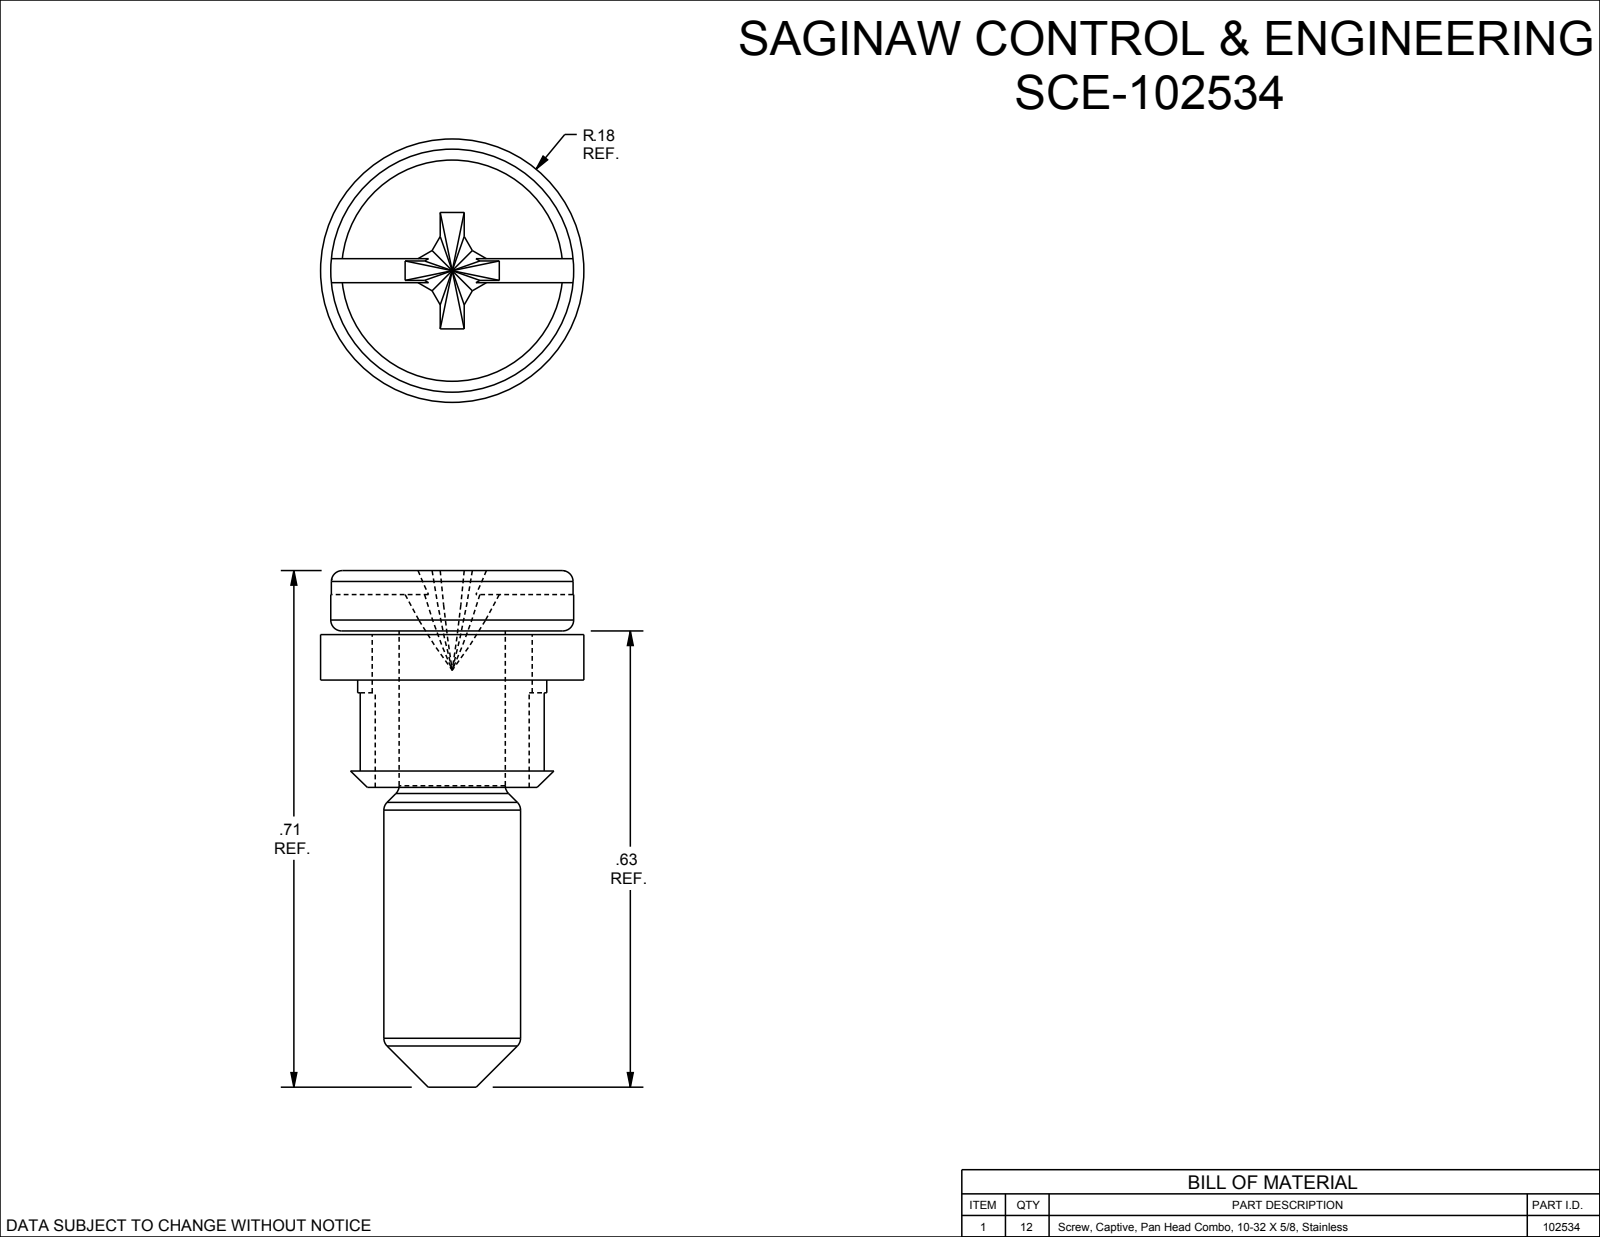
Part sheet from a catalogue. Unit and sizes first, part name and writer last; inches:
Units: inches
Overall size (bounding box): 0.71 × 0.362 × 0.362
Round holes (diameter × count): ⌀0.22 ×1
Round bosses / shafts (diameter × count): ⌀0.362 ×1, ⌀0.334 ×1, ⌀0.26 ×1, ⌀0.188 ×1, ⌀0.146 ×1
Main face-to-face distances: 0.088, 0.083, 0.063, 0.068, 0.151, 0.033, 0.013, 0.046, 0.125, 0.187
Volume: 0.026 in³ · Surface area: 1.077 in²
Bodies: 2 solids, 58 faces (22 planar, 6 cylindrical, 30 other)
Part name (STEP PRODUCT): SCE-102534
STEP written by: SolidWorks 2019 (AUTOMOTIVE_DESIGN)
